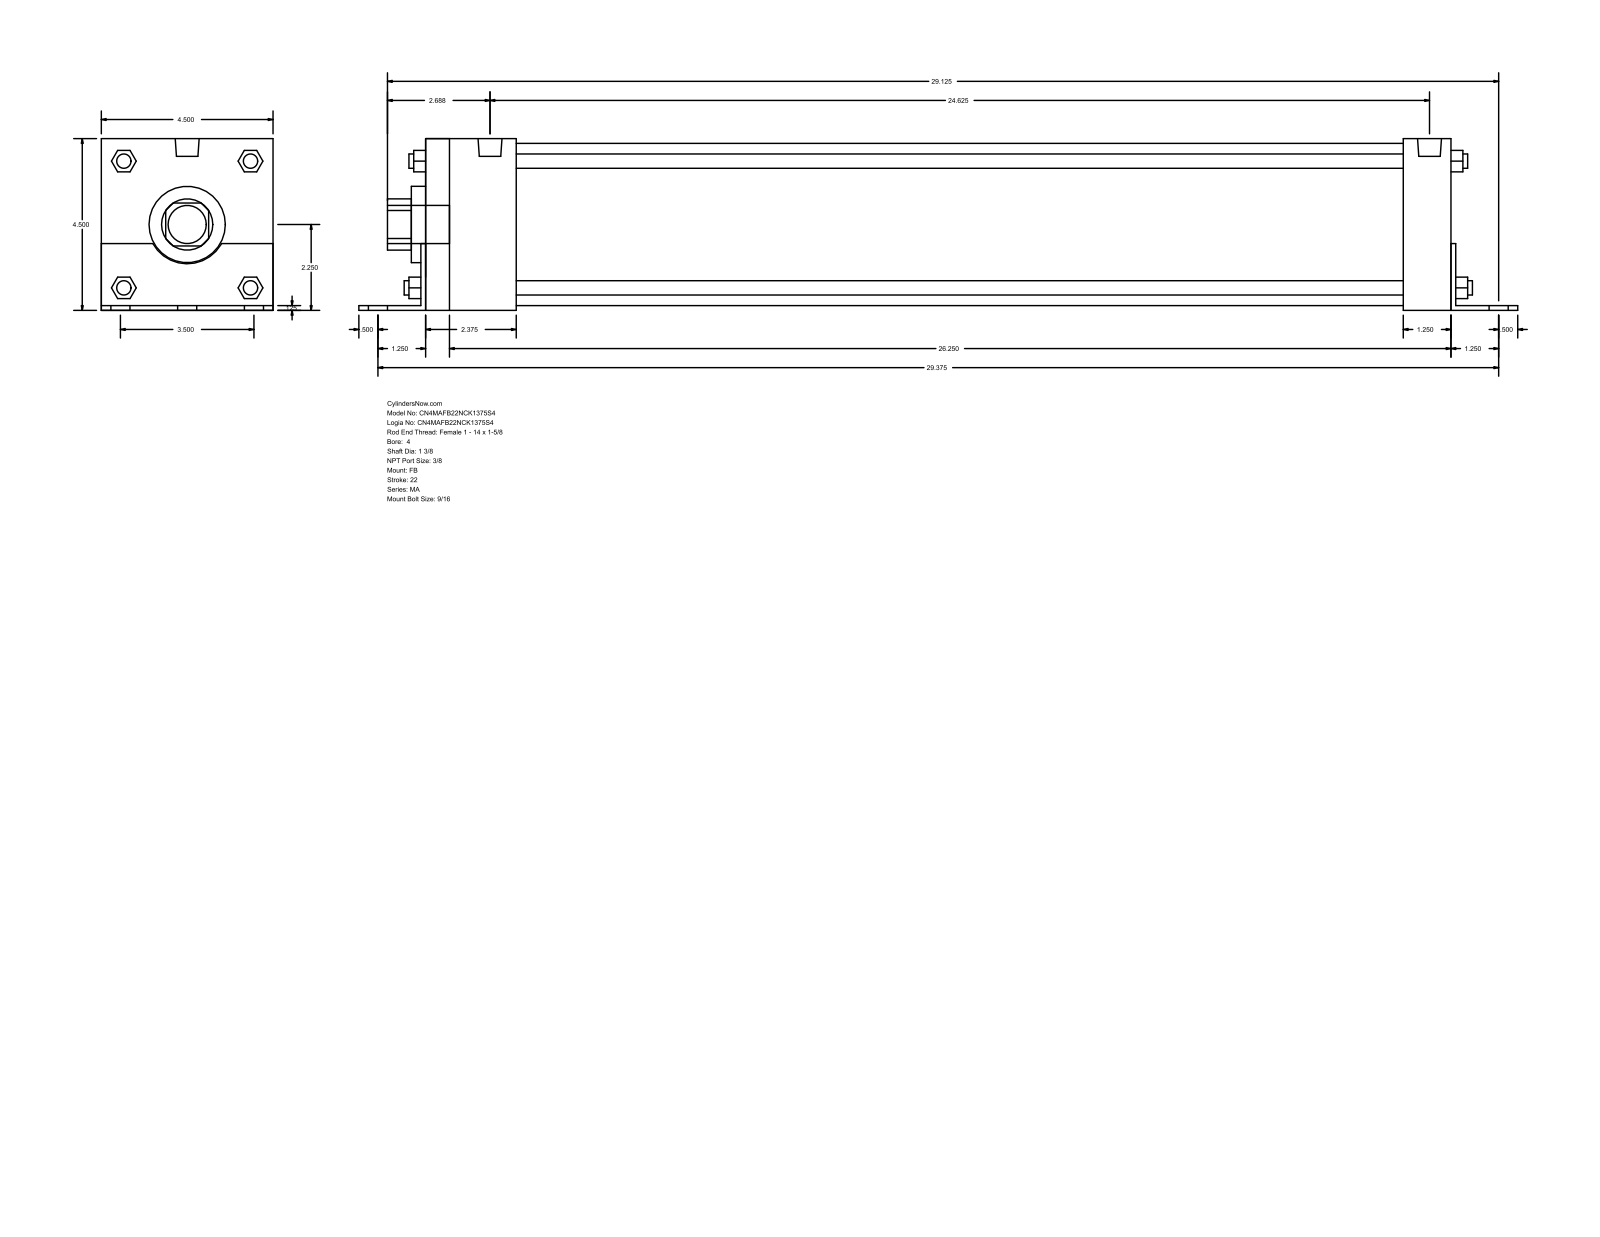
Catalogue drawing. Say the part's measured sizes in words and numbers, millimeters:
The part is named "MA_FB__0400_1.375". Its 3-D file was written by "GSSL Pune (CONFIG_CONTROL_DESIGN)". It is 0 solids with 140 faces: 105 planar, 35 cylindrical and 0 other. Overall it measures 771.52 by 114.35 by 114.3 millimeters. Round holes: 1 of diameter 34.92, 1 of diameter 50.8, 1 of diameter 107.95. Round bosses or shafts: 6 of diameter 14.29, 4 of diameter 11.11, 4 of diameter 9.53, 2 of diameter 15.93, 1 of diameter 25.4. Partial cylindrical surfaces (rounded edges, fillets, slot ends): 1 of radius 17.06, 1 of radius 26.16. The main face-to-face distances are 114.3, 3.17, 114.35, 3.12, 111.18, 682.62, 3.18, 685.8, 34.93, 60.32.
